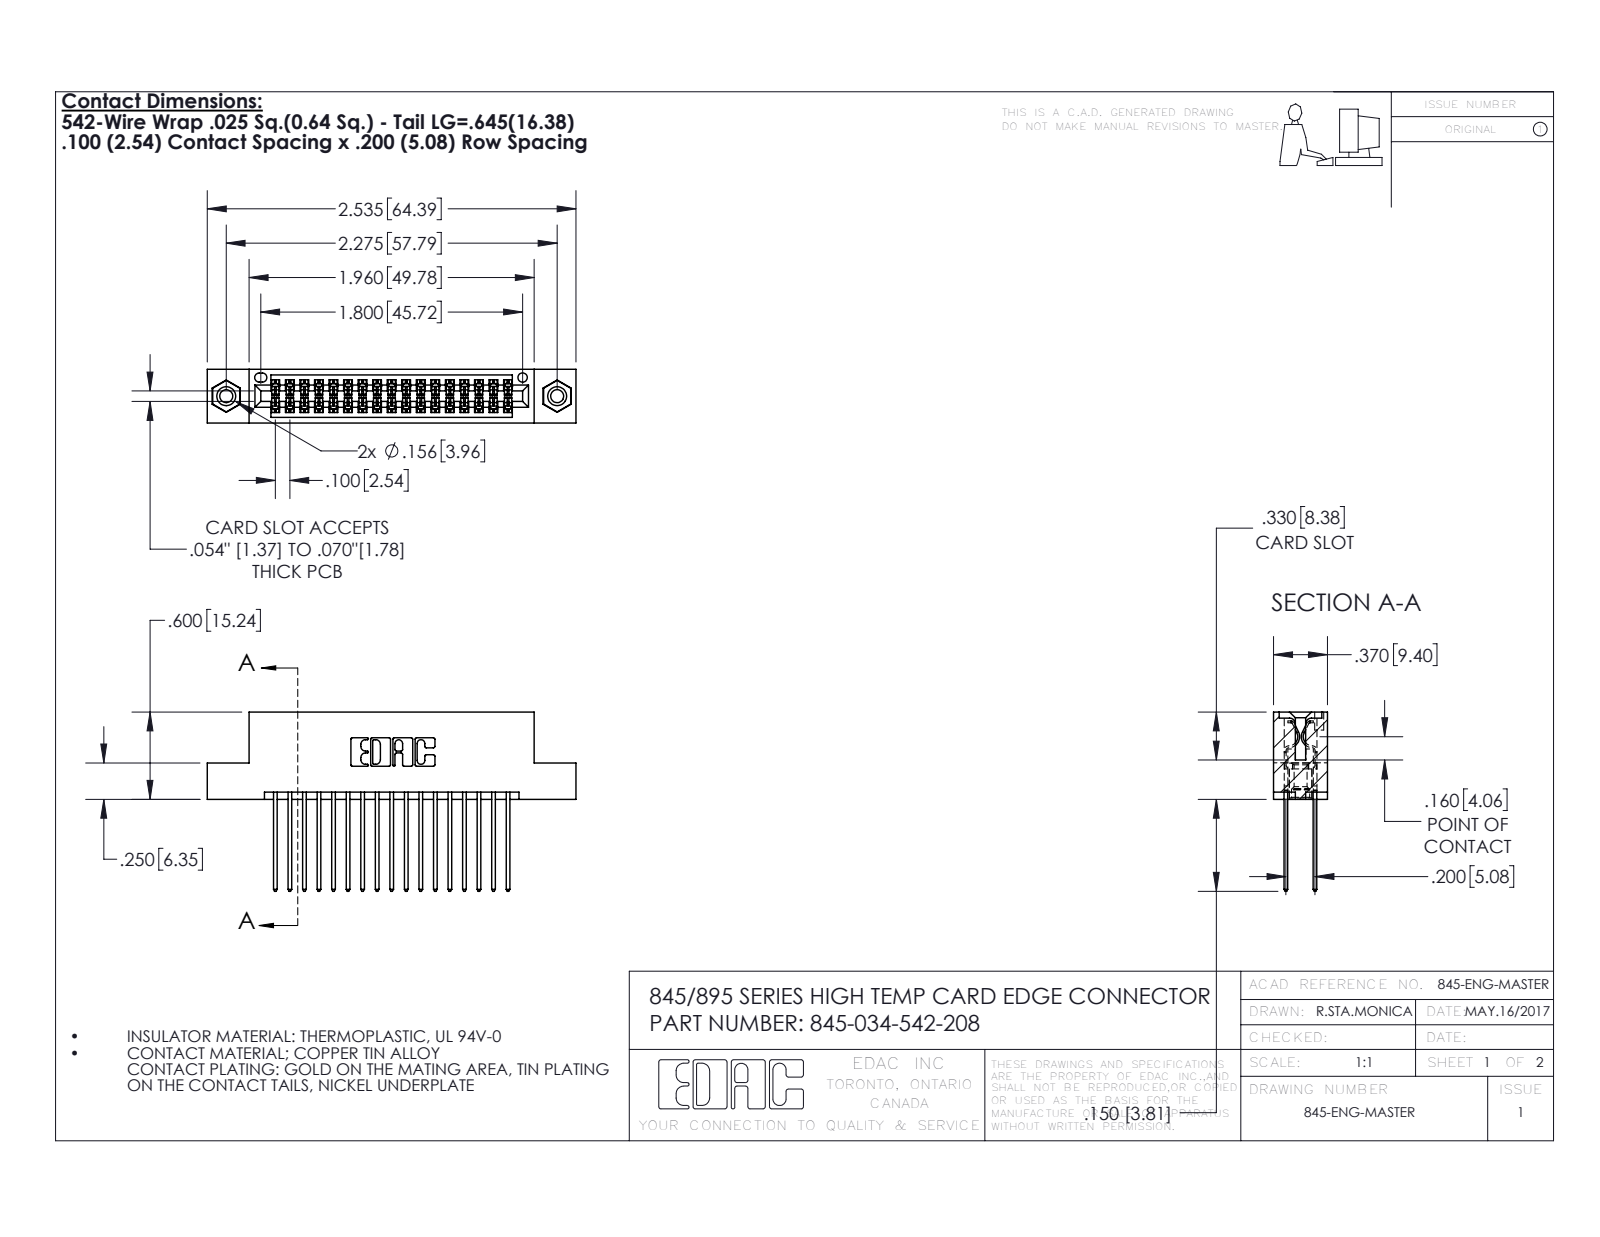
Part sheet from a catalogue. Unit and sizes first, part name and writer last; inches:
Units: inches
Overall size (bounding box): 2.535 × 1.232 × 0.37
Round holes (diameter × count): ⌀0.089 ×2, ⌀0.125 ×2, ⌀0.156 ×2, ⌀0.064 ×1
Round bosses / shafts (diameter × count): ⌀0.155 ×2
Partial cylindrical surfaces — rounded edges, fillets, slot ends (radius × count): R0.006 ×51, R0.01 ×34, R0.01 ×22, R0.007 ×6, R0.031 ×6, R0.026 ×3, R0.014 ×2, R0.019 ×2
Main face-to-face distances: 0.072, 0.298, 0.2, 0.098, 0.272, 0.025, 0.37, 0.225, 0.175, 0.1
Hole centre spacings: 0.27, 2.041, 2.275
Volume: 0.377 in³ · Surface area: 14.57 in²
Bodies: 37 solids, 1886 faces (1234 planar, 636 cylindrical, 16 other)
Part name (STEP PRODUCT): 345-034-542-208; 345 Part_Flush Mounting Lugs - 0.156 Dia-TI; 345-250-001_345-250-003-102; 345-292-001_345-293-142
STEP written by: SolidWorks 2016 (CONFIG_CONTROL_DESIGN)
